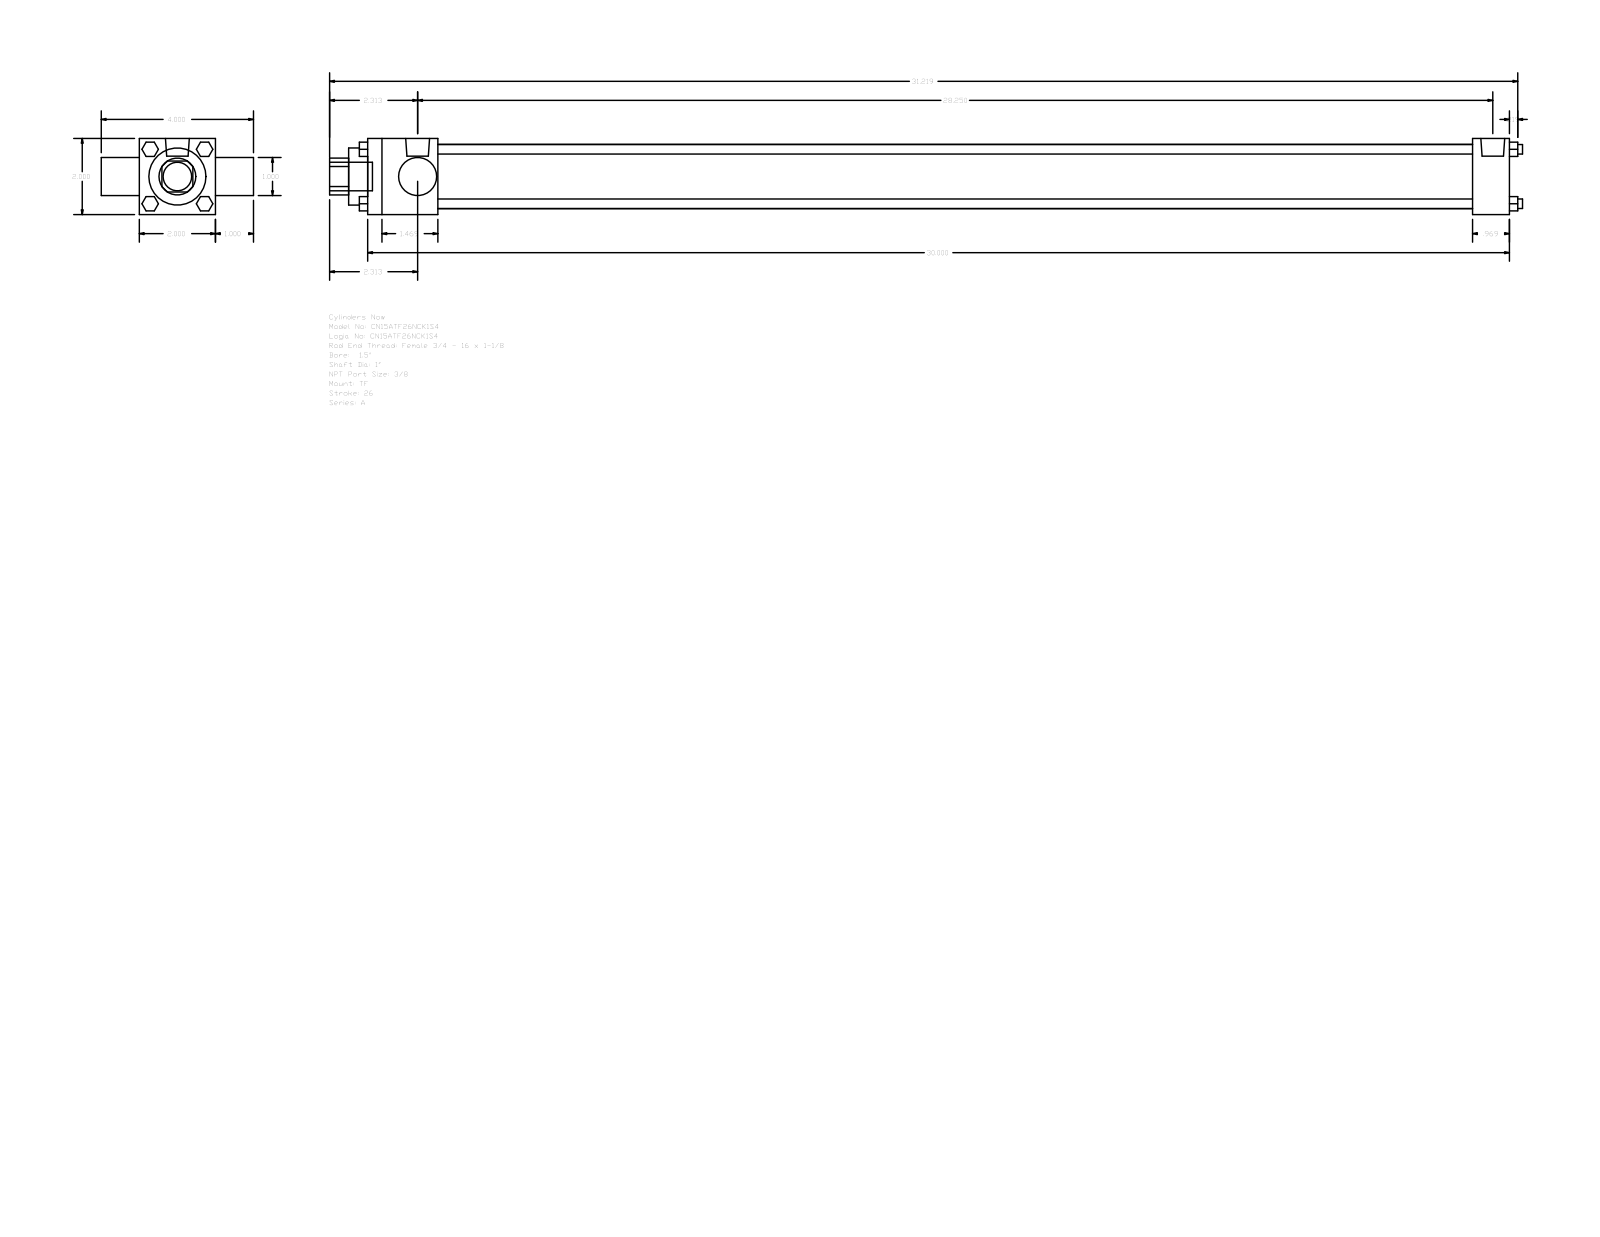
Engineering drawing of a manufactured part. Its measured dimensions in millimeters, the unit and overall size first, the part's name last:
Units: millimetres
Overall size (bounding box): 796.13 × 101.6 × 50.8
Round holes (diameter × count): ⌀25.4 ×2, ⌀38.1 ×1, ⌀42.93 ×1
Round bosses / shafts (diameter × count): ⌀6.35 ×4, ⌀5.56 ×3, ⌀15.93 ×2, ⌀19.05 ×1
Partial cylindrical surfaces — rounded edges, fillets, slot ends (radius × count): R12.29 ×1
Main face-to-face distances: 50.8, 25.4, 762, 76.2, 46.83, 737.39, 690.56, 715.17, 24.61, 12.7
Bodies: 0 solids, 120 faces (92 planar, 28 cylindrical, 0 other)
Part name (STEP PRODUCT): A_TF__0150_1
STEP written by: GSSL Pune (CONFIG_CONTROL_DESIGN)
